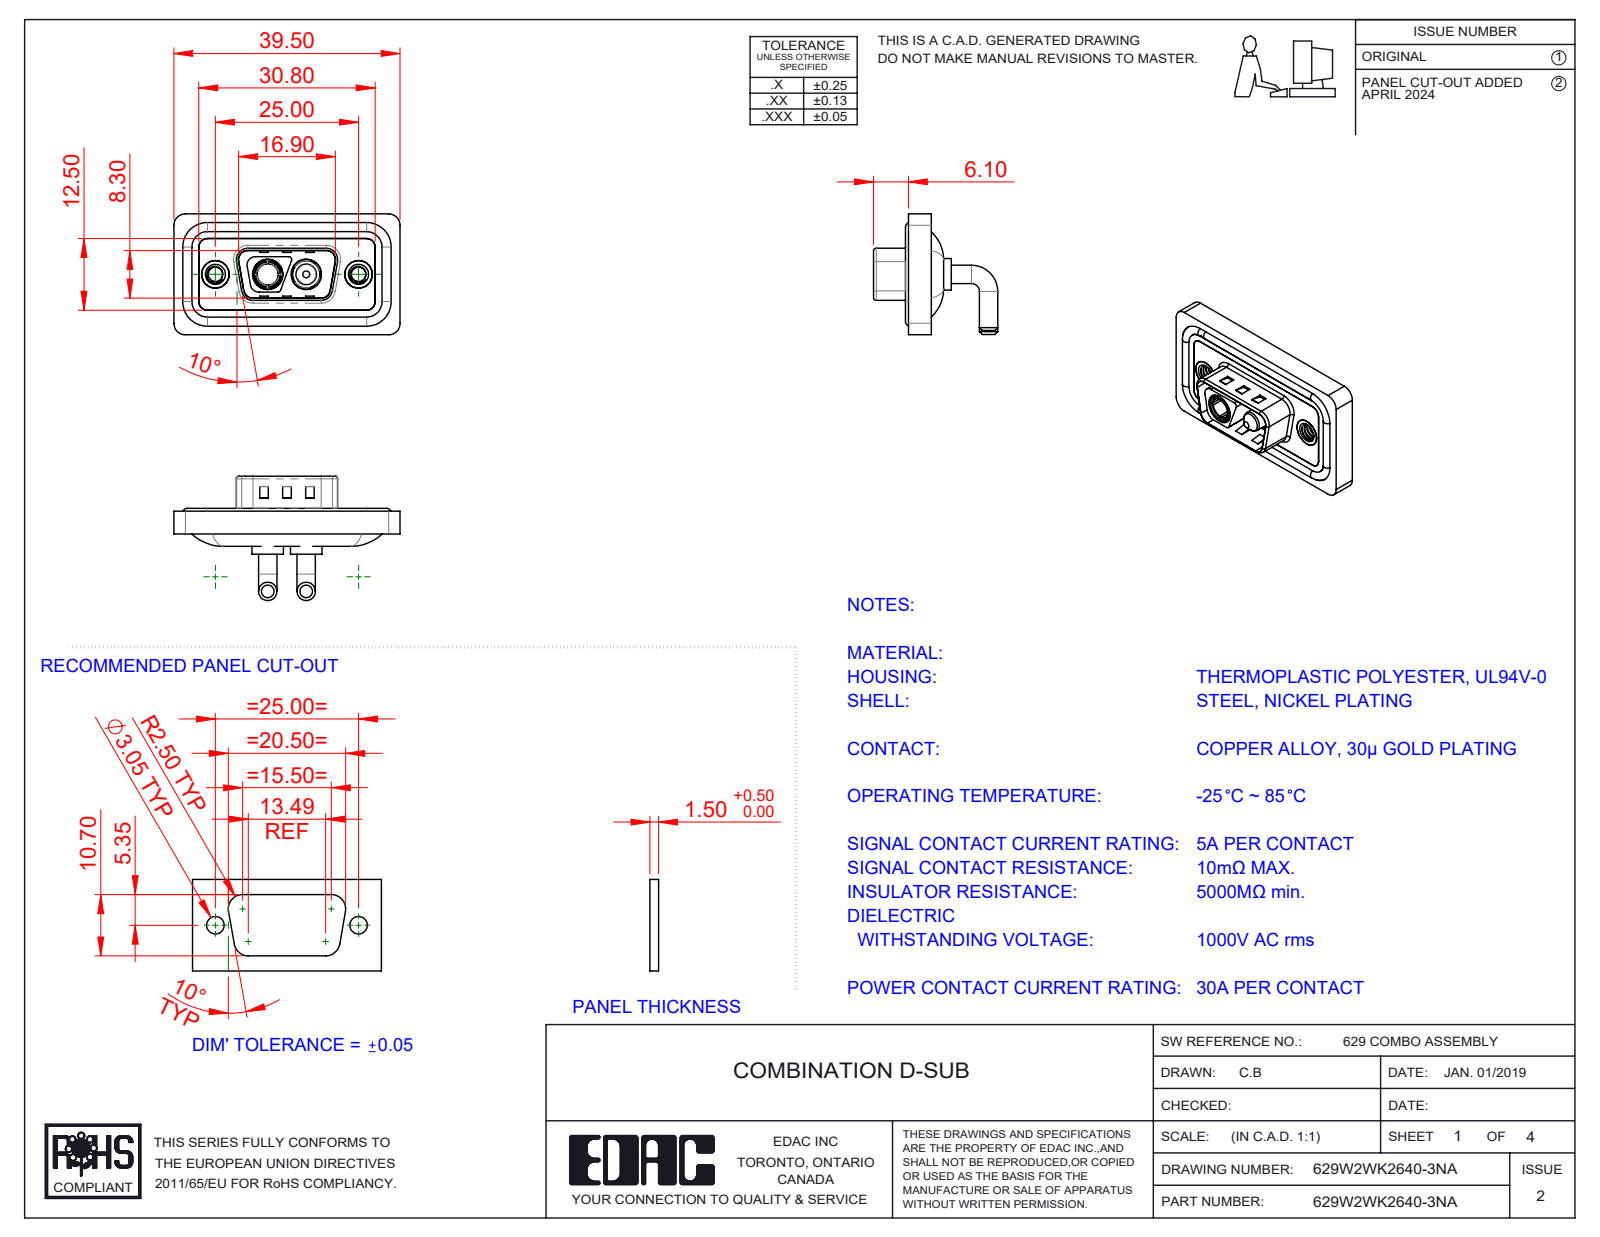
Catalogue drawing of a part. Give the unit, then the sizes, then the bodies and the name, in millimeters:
Units: millimetres
Overall size (bounding box): 39.5 × 21.7 × 21.1
Round holes (diameter × count): ⌀2.5 ×2, ⌀4 ×2, ⌀4.8 ×2, ⌀4.85 ×2, ⌀5 ×2, ⌀5.3 ×2, ⌀3.7 ×1
Round bosses / shafts (diameter × count): ⌀3.2 ×4, ⌀1.6 ×4, ⌀5.5 ×2, ⌀5.2 ×2, ⌀4.9 ×2, ⌀4.75 ×2, ⌀3.75 ×2, ⌀4.96 ×1
Partial cylindrical surfaces — rounded edges, fillets, slot ends (radius × count): R1.5 ×20, R2 ×18, R0.5 ×10, R1.6 ×8, R0.25 ×4, R0.6 ×4, R0.65 ×4, R0.9 ×4
Main face-to-face distances: 0.4, 2.9, 1.1, 0.8, 2.1, 2.5, 3.1, 1.6, 4.5, 1.5
Hole centre spacings: 9.14, 15.86, 6.72, 25
Volume: 4 743 mm³ · Surface area: 7 573 mm²
Bodies: 11 solids, 536 faces (189 planar, 229 cylindrical, 118 other)
Part name (STEP PRODUCT): 629Combo Shell Rear_09 Contacts; 629Combo Housing_2WK2; Power Socket_30A RA; Power Pin_30A RA (+4 more)
STEP written by: SolidWorks 2023 (CONFIG_CONTROL_DESIGN)
